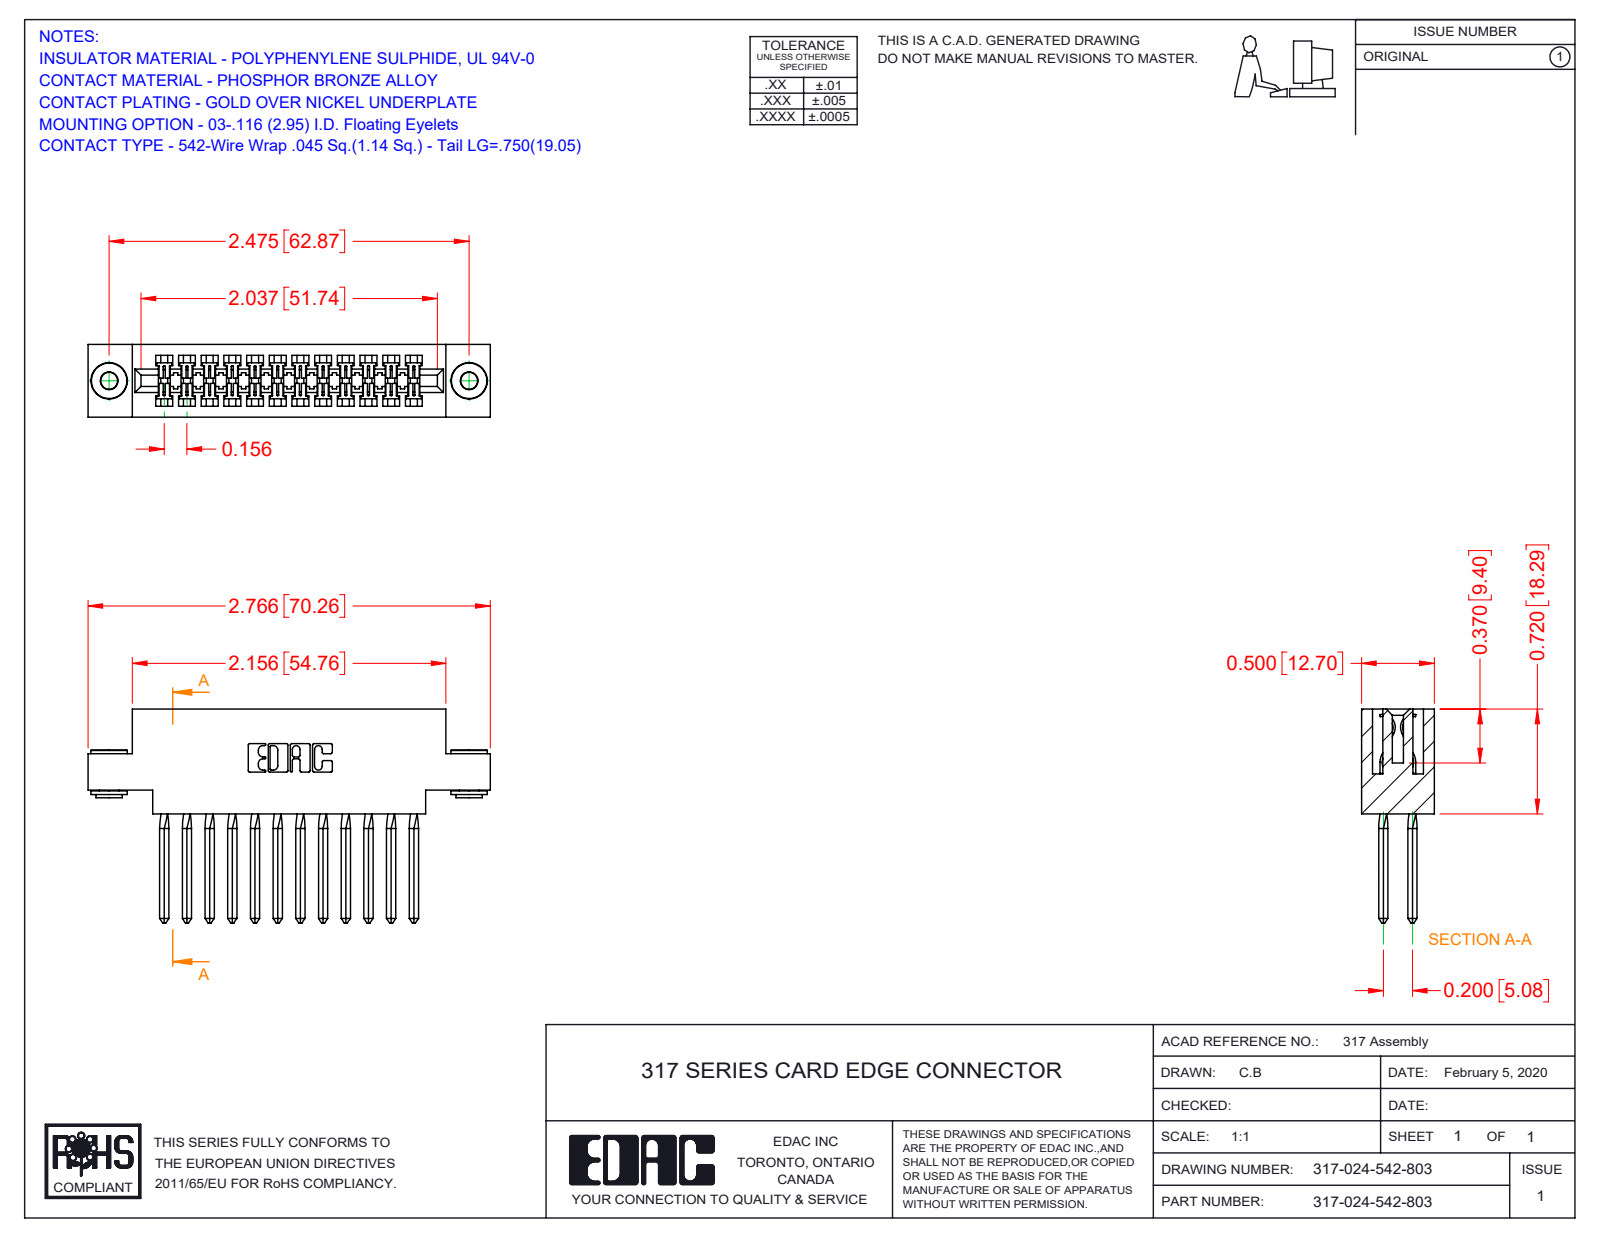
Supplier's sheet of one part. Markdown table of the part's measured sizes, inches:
| quantity | value |
| --- | --- |
| part name | 345-250-002_345-250-002-102; 317-290-003_542; 317 Part_.156 Dia - TH; 317-024-542-803 |
| STEP written by | SolidWorks 2016 (CONFIG_CONTROL_DESIGN) |
| units | inches |
| bodies | 27 solids, 1508 faces (1172 planar, 232 cylindrical, 104 other) |
| overall size | 2.766 × 1.47 × 0.5 |
| volume | 0.645 in³ |
| surface area | 21.64 in² |
| round holes (diameter × count) | 0.116 × 2, 0.156 × 2 |
| round bosses / shafts (diameter × count) | 0.25 × 2, 0.18 × 2, 0.136 × 2 |
| partial cylindrical surfaces (radius × count) | 0.006 × 48, 0.01 × 22, 0.007 × 6, 0.031 × 6, 0.026 × 3, 0.074 × 2, 0.089 × 2, 0.1 × 2 |
| main face-to-face distances | 0.5, 0.075, 0.425, 0.11, 0.35, 0.22, 0.116, 0.2, 0.136, 0.305 |
| hole center spacings | 2.475 |
